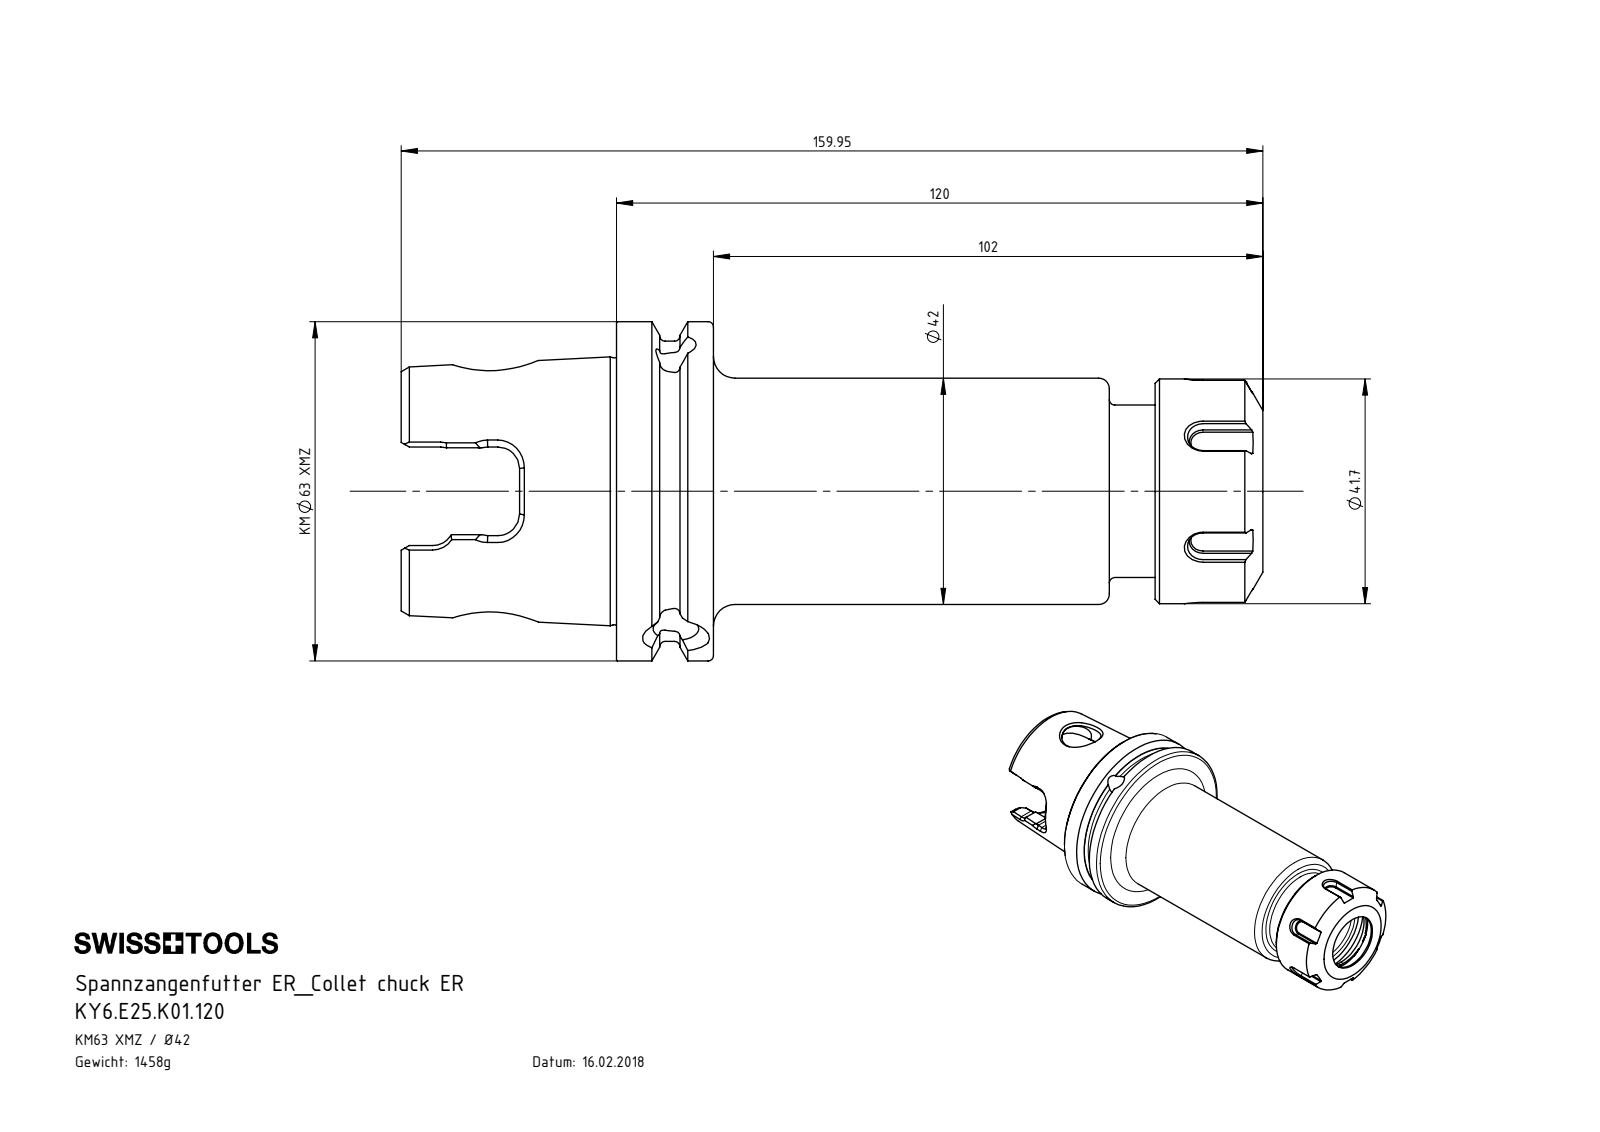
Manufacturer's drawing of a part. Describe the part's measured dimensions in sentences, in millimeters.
The part is named "E25-ER1.001.020; KY6-E25.K01.120_B; KY6.E25.K01.120". Its 3-D file was written by "SolidWorks 2017 (CONFIG_CONTROL_DESIGN)". It is 2 solids with 325 faces: 96 planar, 68 cylindrical and 161 other. Overall it measures 159.95 by 62.95 by 62.95 millimeters. Its volume is 185 703 cubic millimeters and its surface area 41 583 square millimeters. Round holes: 2 of diameter 7.47, 1 of diameter 8, 1 of diameter 8.48, 1 of diameter 10, 1 of diameter 11.5, 1 of diameter 14, 1 of diameter 14.5, 1 of diameter 16.5, 1 of diameter 18, 1 of diameter 20.9, 1 of diameter 30.5, 1 of diameter 31.1. Round bosses or shafts: 1 of diameter 62.95, 1 of diameter 55.7, 1 of diameter 42, 1 of diameter 41.7, 1 of diameter 32. Partial cylindrical surfaces (rounded edges, fillets, slot ends): 6 of radius 4, 2 of radius 7.04, 2 of radius 12.17. The main face-to-face distances are 18, 1.1, 19.1, 101.1, 100, 82, 121.1, 120, 102, 20.
